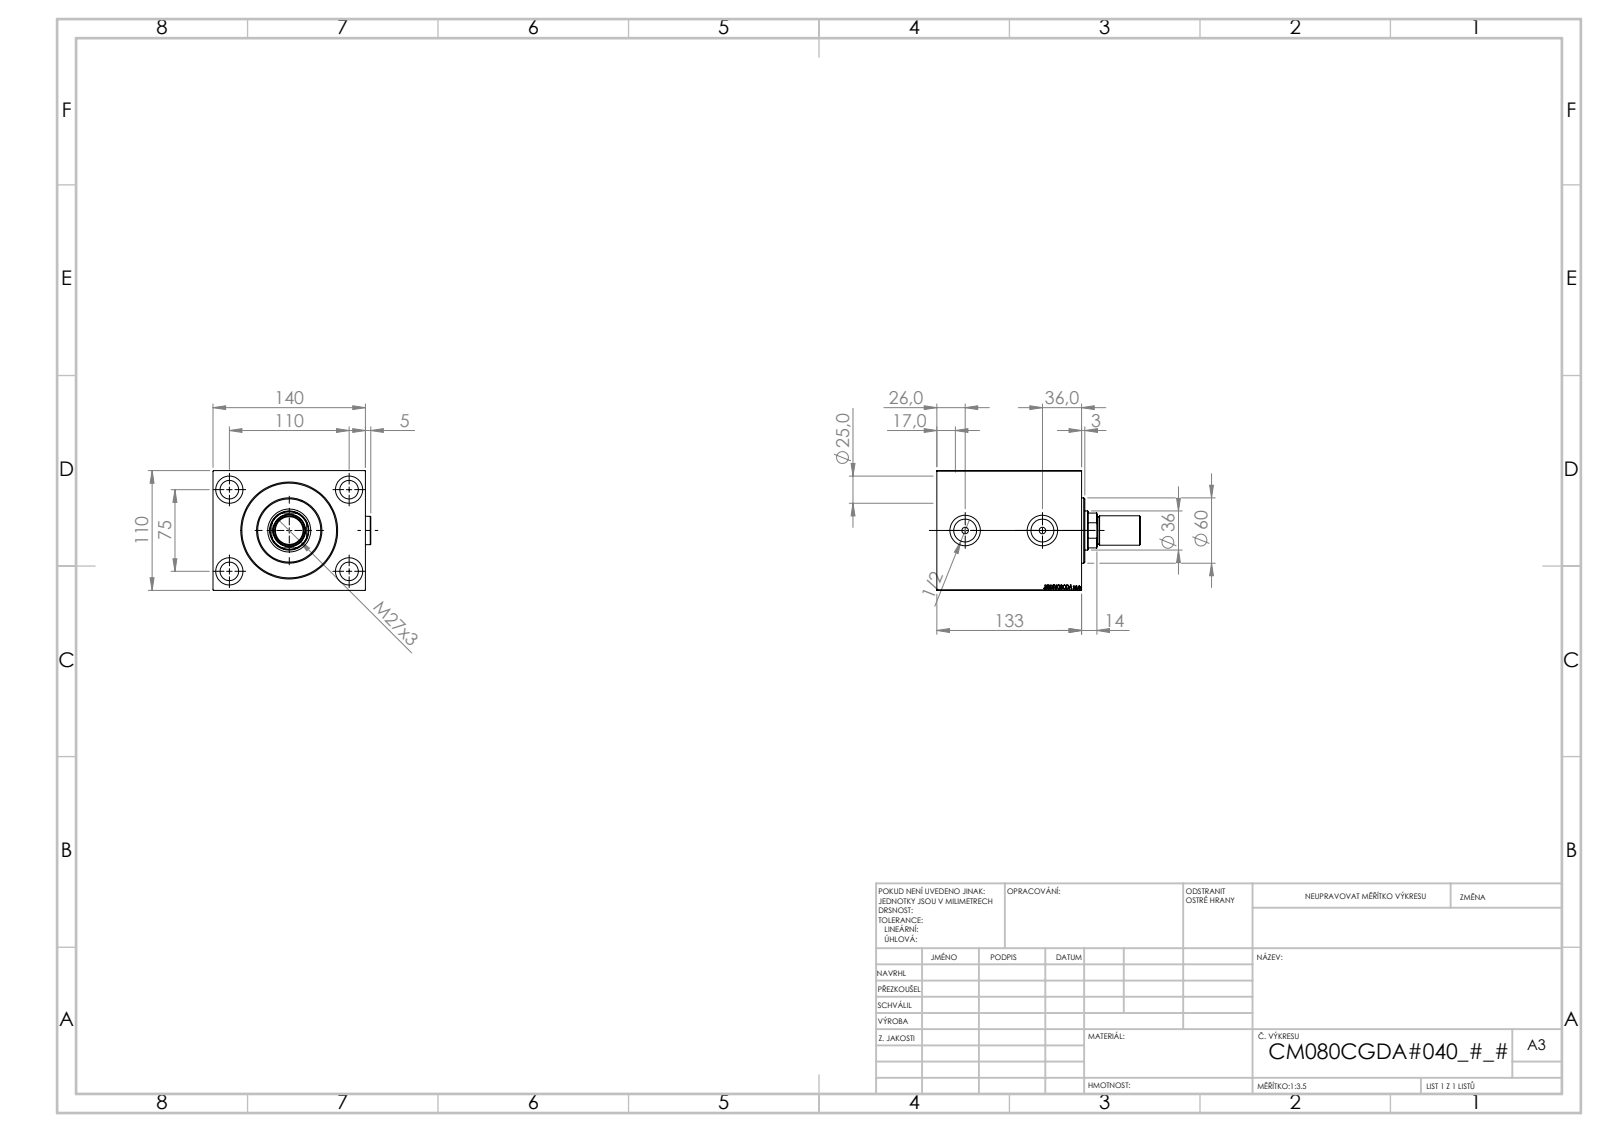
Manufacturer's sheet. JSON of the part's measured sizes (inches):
{"part_name": "V450CM_C_Body; V450CM_MALE_METRIC; V450CM_C_VCP; V450CM_VC_B (+1 more)", "step_written_by": "SolidWorks 2019 (CONFIG_CONTROL_DESIGN)", "units": "inches", "bodies": {"solids": 6, "faces": 933, "planar": 447, "cylindrical": 82, "other": 404}, "overall_size": [7.362, 5.705, 4.331], "volume_in3": 106.1, "surface_area_in2": 339, "round_holes": [[0.669, 4], [0.984, 4], [0.236, 2], [0.825, 2], [1.102, 2], [1.004, 1], [1.417, 1], [1.555, 1], [3.15, 1], [3.228, 1], [3.425, 1]], "round_bosses_or_shafts": [[1.024, 2], [2.362, 1], [1.063, 1], [0.984, 1]], "partial_cylinders_radius": [[0.689, 1]], "face_to_face_distances": [4.331, 5.512, 5.236, 4.409, 0.827, 0.551, 4.685, 2.126, 3.858, 1.575], "hole_center_spacings": [2.621, 2.953, 4.331, 5.242, 2.795]}
